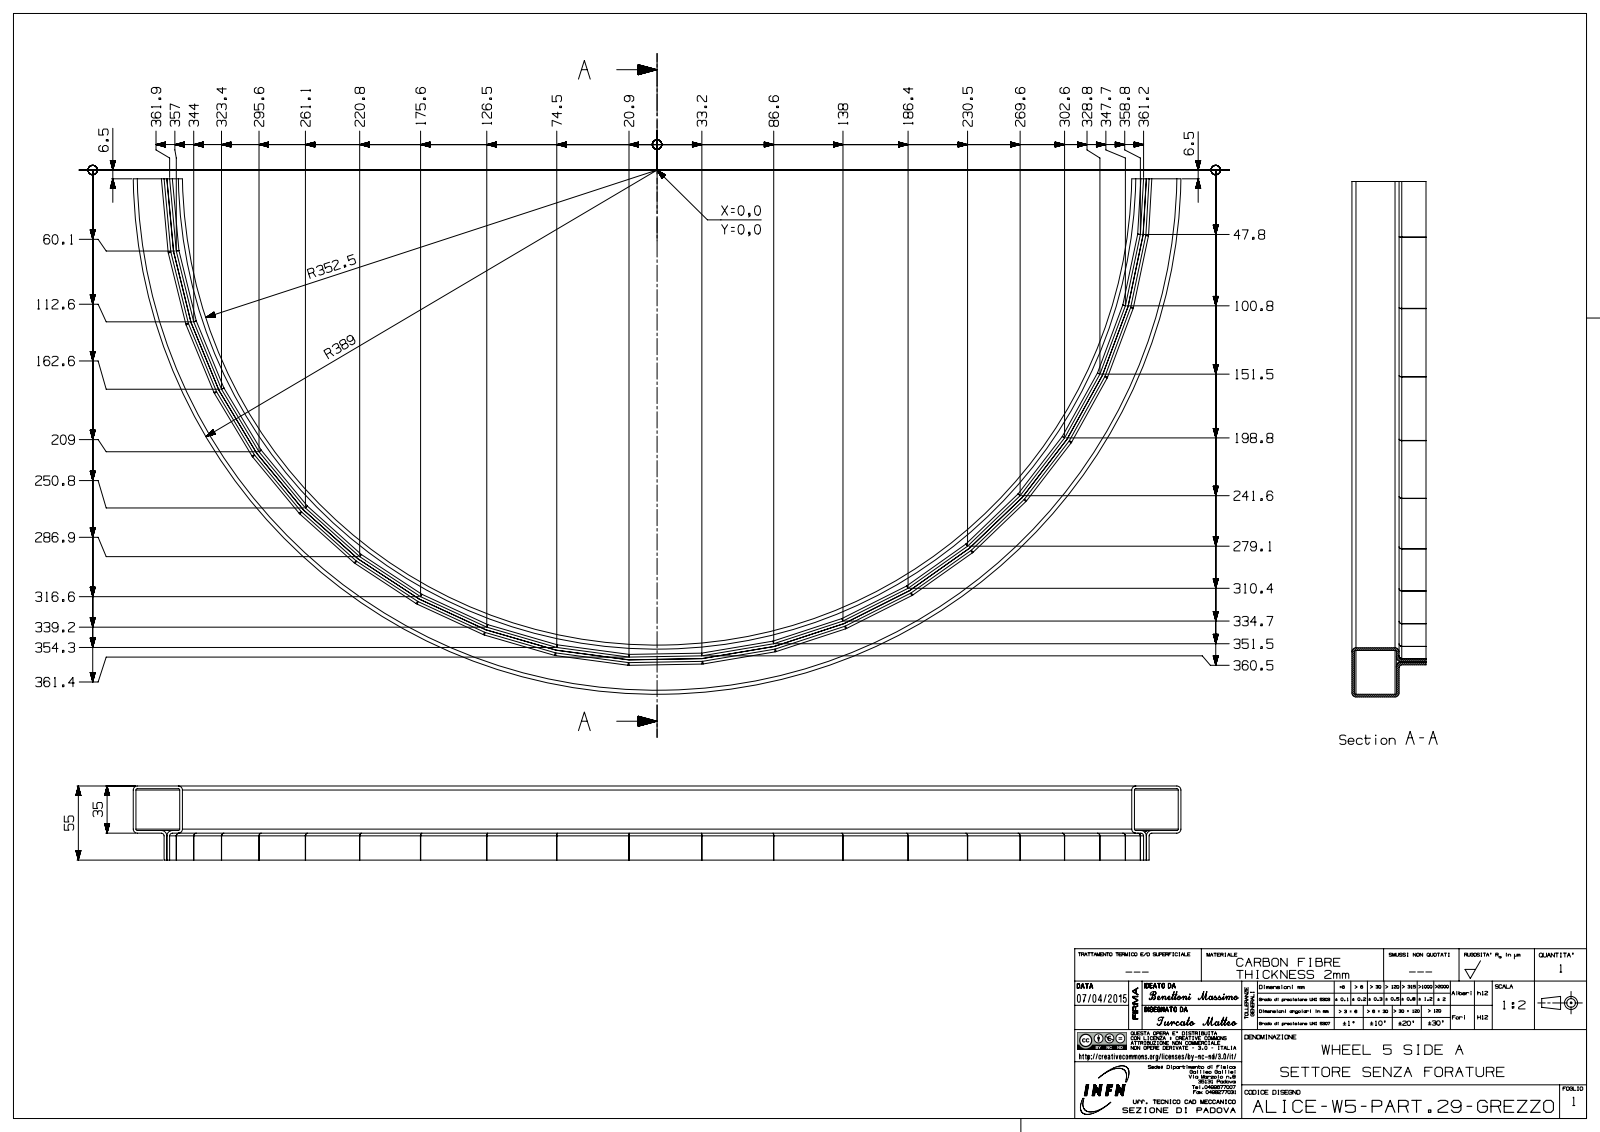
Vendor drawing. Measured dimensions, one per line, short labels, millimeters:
name: turc1B407CEDsckq
written by: SIEMENS PLM Software NX 8.5 (AP203_CONFIGURATION_CONTROLLED_3D_DESIGN_OF_MECHANICAL_PARTS_AND_ASSEMBLIES_MIM_LF)
unit: mm
bodies: 1 solid, 350 faces (94 planar, 168 cylindrical, 88 other)
size: 777.89 × 382.5 × 55
volume: 387 370 mm³; area: 392 584 mm²
rounds: 82× R4, 62× R2, 20× R4.1, 1× R352.5, 1× R354.5, 1× R387, 1× R389
face distances: 2, 33, 2.1, 31, 35, 4.1, 55, 53, 22, 20
